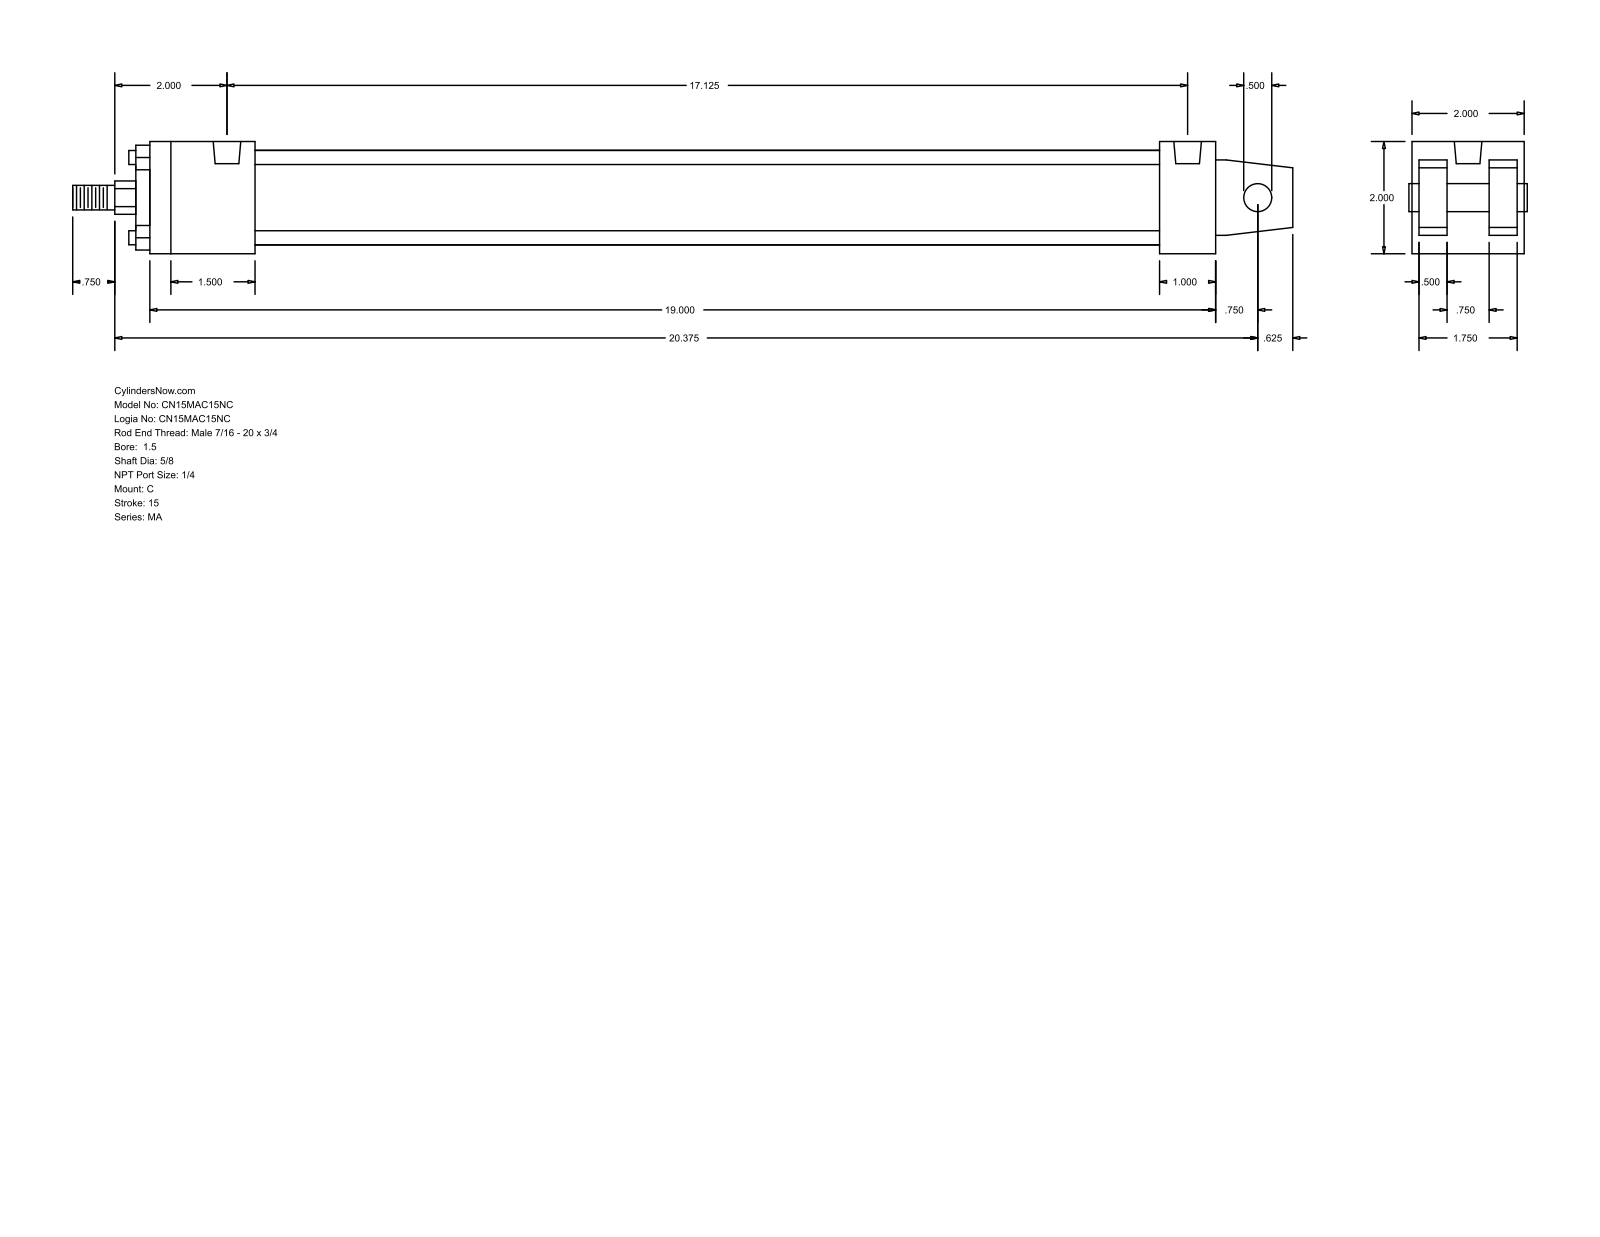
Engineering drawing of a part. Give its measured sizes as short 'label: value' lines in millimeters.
name: MA_C__0150_0.625
written by: GSSL Pune (CONFIG_CONTROL_DESIGN)
unit: mm
bodies: 0 solids, 103 faces (76 planar, 27 cylindrical, 0 other)
size: 552.45 × 50.8 × 50.8
holes: 4× ⌀7.94, 2× ⌀12.49
bosses: 4× ⌀6.35, 1× ⌀42.93, 1× ⌀28.57, 1× ⌀15.88, 1× ⌀12.7, 1× ⌀11.11
rounds: 1× R7.54
face distances: 50.8, 12.7, 34.93, 15.87, 3.17, 47.63, 31.76, 482.6, 457.19, 25.41
hole spacings: 434.97
